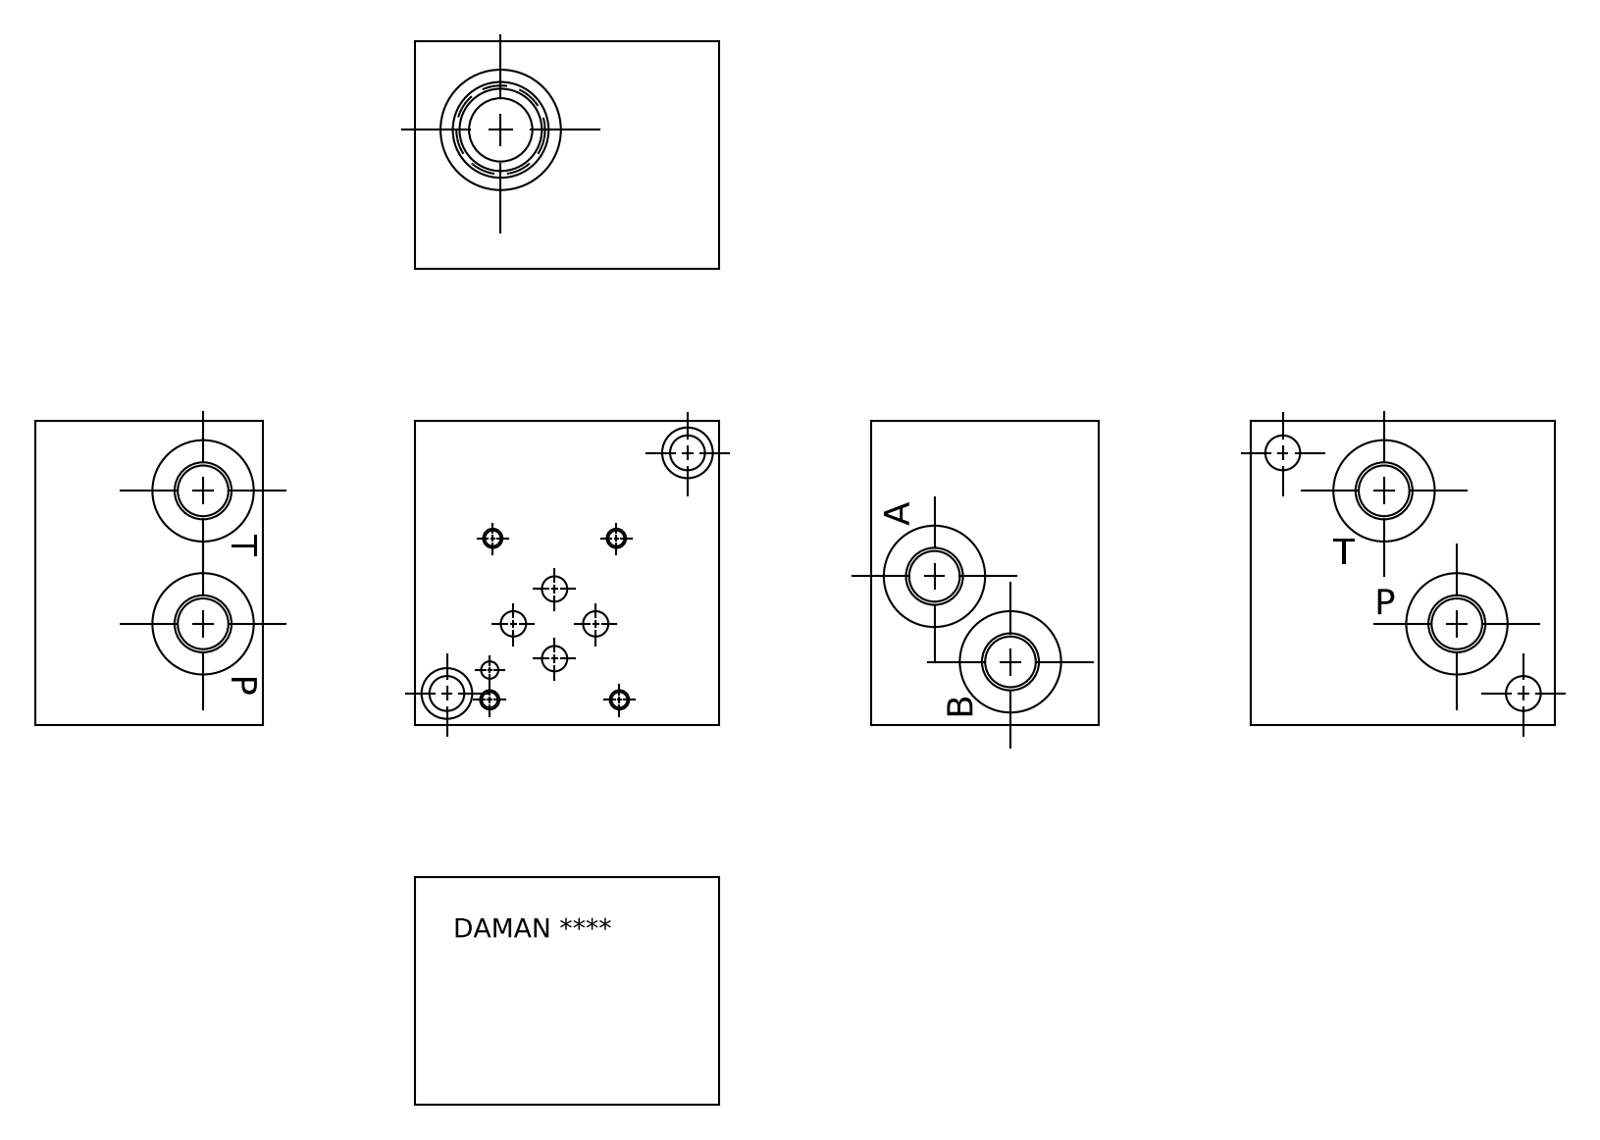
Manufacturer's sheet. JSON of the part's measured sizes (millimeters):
{"part_name": "Part__D03SPRVC6S_3D", "step_written_by": "Autodesk Inventor 2020 (AUTOMOTIVE_DESIGN)", "units": "millimeters", "bodies": {"solids": 1, "faces": 563, "planar": 313, "cylindrical": 53, "other": 197}, "overall_size": [76.2, 76.2, 57.15], "volume_mm3": 280984, "surface_area_mm2": 42191, "round_holes": [[14.27, 6], [14.53, 6], [25.02, 6], [12.29, 5], [12.9, 5], [3.78, 4], [4.83, 4], [7.14, 4], [8.74, 2], [12.7, 2], [3.96, 1], [12.9, 1]], "partial_cylinders_radius": [[6.15, 1]], "face_to_face_distances": [76.2, 57.15, 0.79, 75.41, 3.17, 53.98, 74.62, 67.97, 8.23, 12.7], "hole_center_spacings": [13.52, 13.54, 22.05, 33.55, 40.5, 51.45, 7.49, 10.86]}
